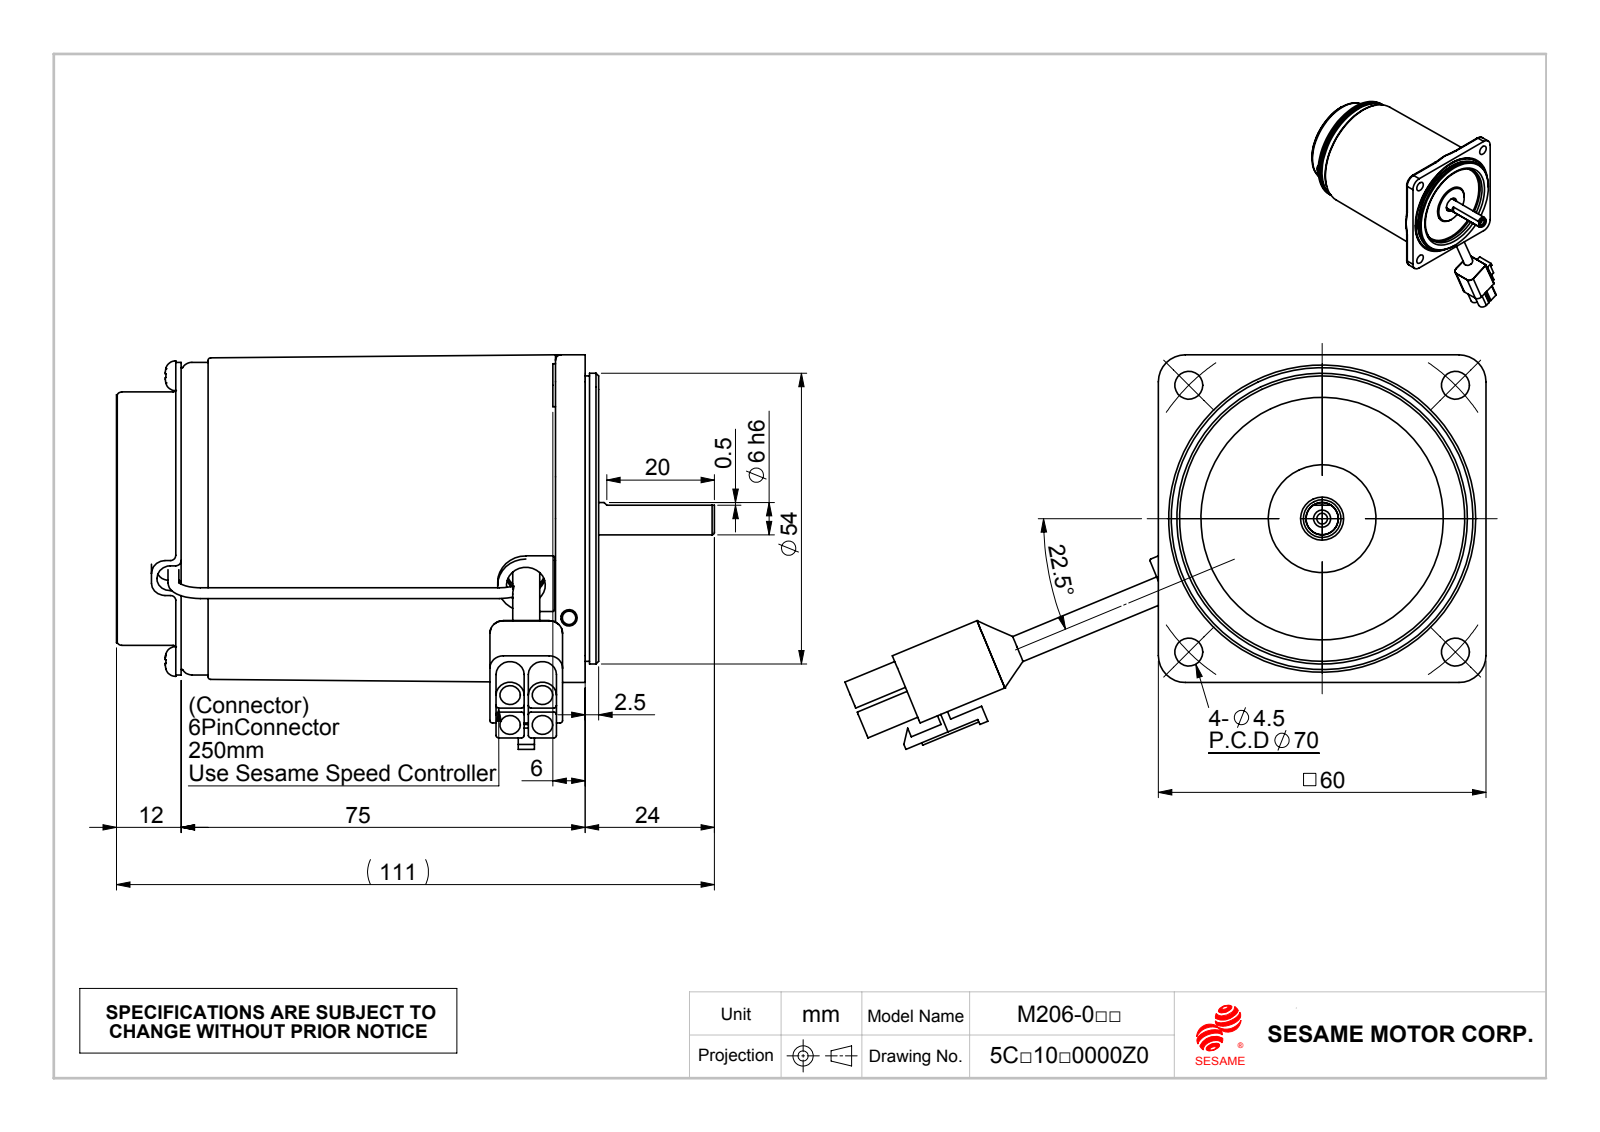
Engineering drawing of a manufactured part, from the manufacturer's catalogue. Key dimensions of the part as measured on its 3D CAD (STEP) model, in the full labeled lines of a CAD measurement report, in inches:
Part name (STEP PRODUCT): M206-RK-R_Default; 公端子; C254_Default; 06A_0成品 (+1 more)
STEP written by: SolidWorks 2010 (CONFIG_CONTROL_DESIGN)
Units: inches
Bodies: 9 solids, 478 faces (166 planar, 197 cylindrical, 115 other)
Overall size (bounding box): 4.684 × 4.37 × 2.882
Volume: 4.957 in³ · Surface area: 86.83 in²
Round holes (diameter × count): ⌀0.098 ×5, ⌀0.126 ×4, ⌀0.15 ×4, ⌀0.205 ×4, ⌀0.217 ×4, ⌀0.079 ×2, ⌀0.102 ×2, ⌀0.122 ×2, ⌀0.276 ×1, ⌀0.283 ×1, ⌀0.374 ×1, ⌀0.591 ×1
Round bosses / shafts (diameter × count): ⌀0.315 ×4, ⌀0.217 ×2, ⌀0.118 ×2, ⌀0.079 ×2, ⌀2.283 ×1, ⌀2.123 ×1, ⌀2.084 ×1, ⌀1.85 ×1
Partial cylindrical surfaces — rounded edges, fillets, slot ends (radius × count): R0.02 ×14, R0.039 ×10, R0.01 ×8, R0.012 ×8, R0.098 ×7, R0.197 ×4, R0.051 ×2, R0.102 ×2
Main face-to-face distances: 2.933, 2.894, 0.039, 0.118, 2.776, 0.472, 3.366, 0.157, 2.953, 0.591
Hole centre spacings: 1.46, 0.236, 0.482, 0.167, 0.365, 0.369, 0.675, 0.682
